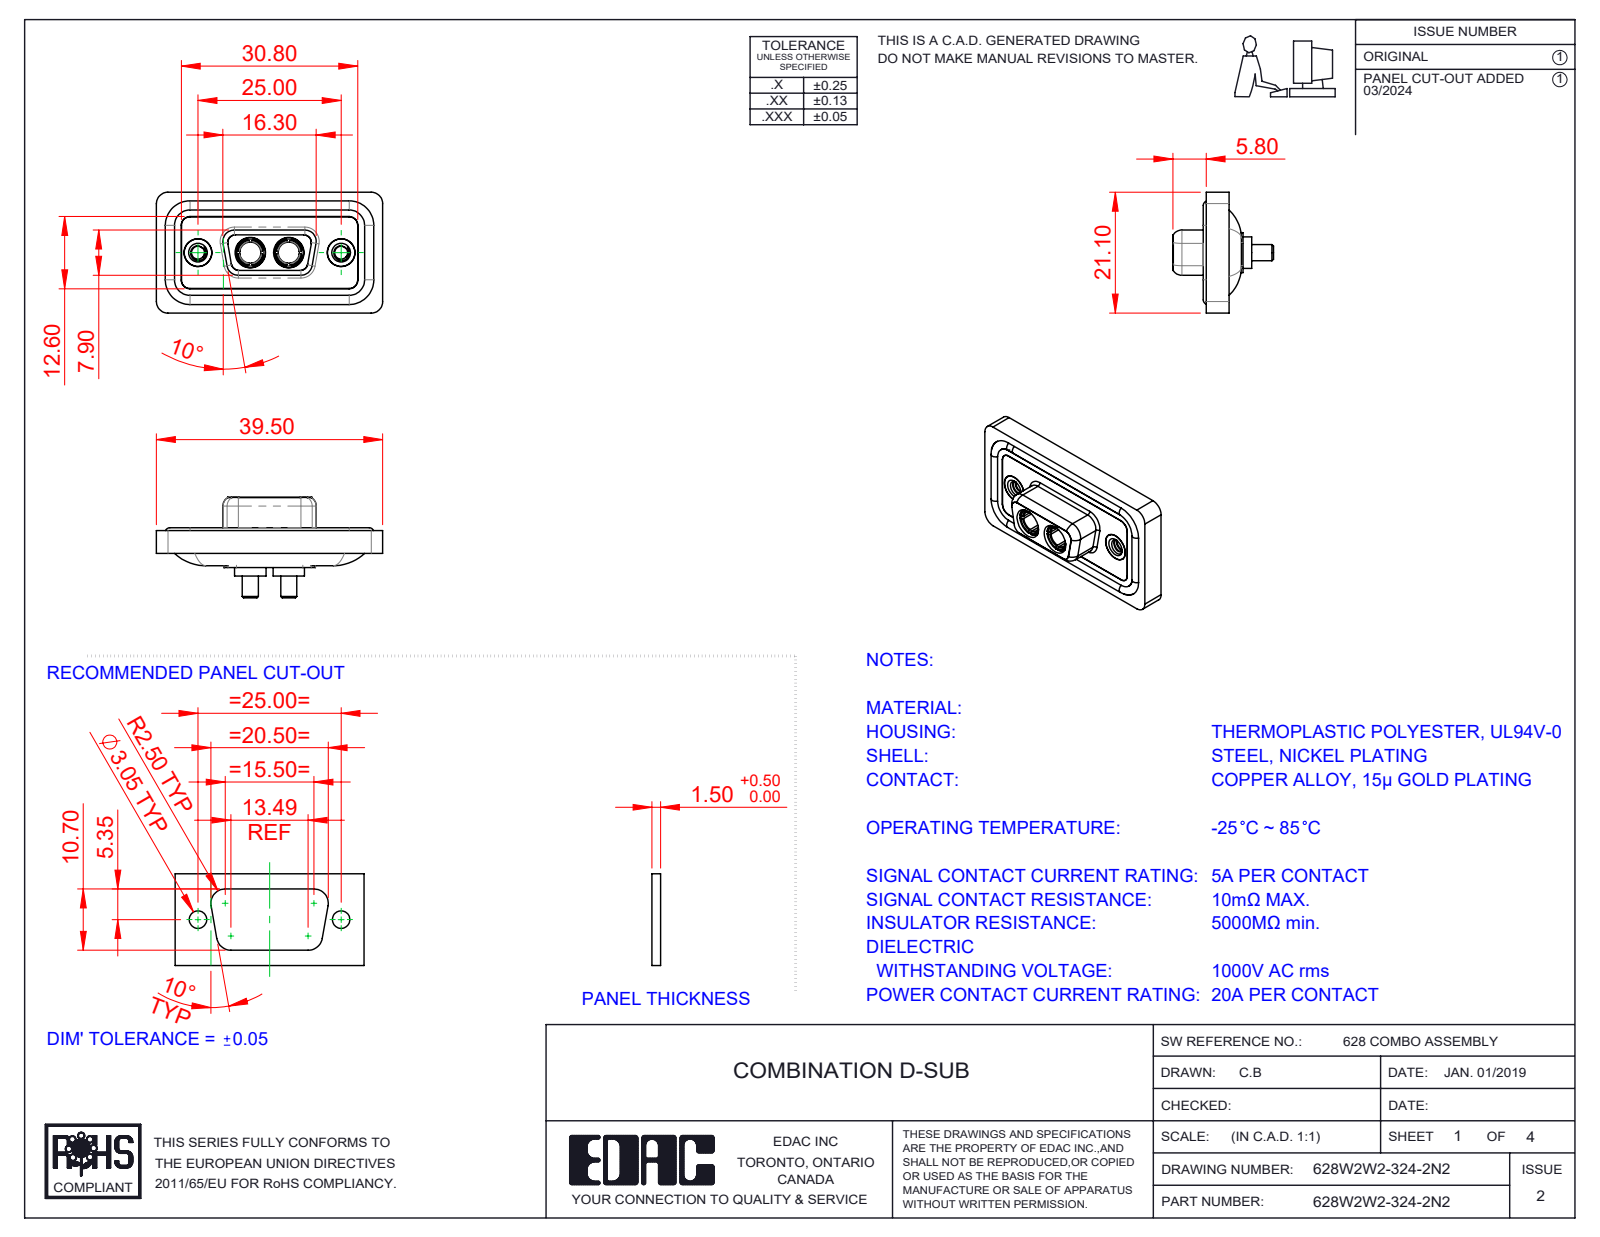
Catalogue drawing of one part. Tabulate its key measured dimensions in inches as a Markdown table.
| quantity | value |
| --- | --- |
| part name | 628Combo Threaded Rivet_2; 628Combo Waterproof Housing_09 Contacts; 628W2W2-324-2N2; 628Combo Housing_2W2 (+3 more) |
| STEP written by | SolidWorks 2023 (CONFIG_CONTROL_DESIGN) |
| units | inches |
| bodies | 11 solids, 534 faces (163 planar, 234 cylindrical, 137 other) |
| overall size | 1.555 × 0.831 × 0.691 |
| volume | 0.288 in³ |
| surface area | 11.84 in² |
| round holes (diameter × count) | 0.191 × 4, 0.089 × 2, 0.146 × 2, 0.157 × 2, 0.159 × 2, 0.197 × 2, 0.209 × 2 |
| round bosses / shafts (diameter × count) | 0.063 × 4, 0.217 × 2, 0.205 × 2, 0.195 × 2, 0.195 × 2, 0.189 × 2, 0.187 × 2, 0.148 × 2 |
| partial cylindrical surfaces (radius × count) | 0.059 × 22, 0.079 × 18, 0.053 × 8, 0.063 × 8, 0.01 × 4, 0.02 × 4, 0.024 × 4, 0.026 × 4 |
| main face-to-face distances | 0.016, 0.071, 0.043, 0.114, 0.02, 0.063, 0.222, 0.293, 0.059, 0.211 |
| hole center spacings | 0.36, 0.624, 0.265, 0.984 |
